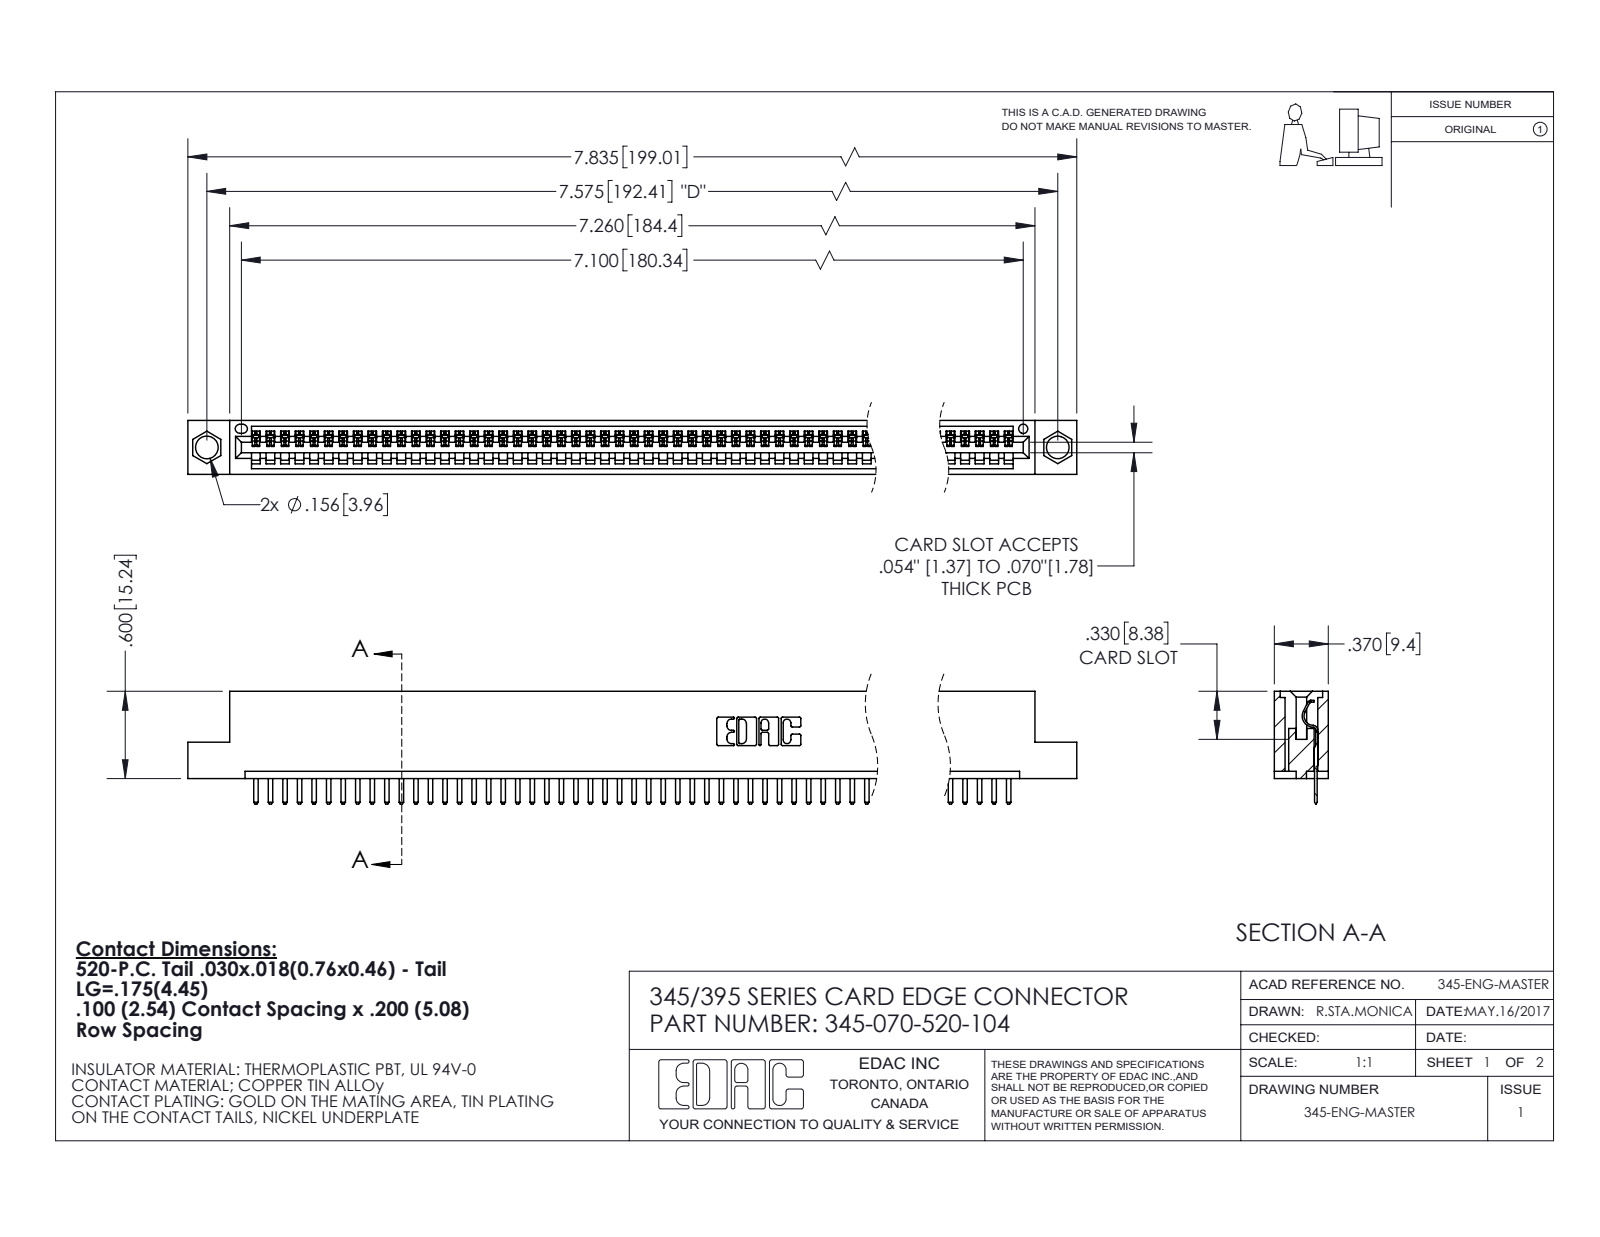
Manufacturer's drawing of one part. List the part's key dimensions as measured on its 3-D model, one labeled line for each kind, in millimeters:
Part name (STEP PRODUCT): 345-070-520-104; 345 Part_Flush Mounting Lugs - 0.156 Dia-TI; 345-292-001_345-293-120
STEP written by: SolidWorks 2020 (CONFIG_CONTROL_DESIGN)
Units: millimetres
Bodies: 71 solids, 4480 faces (3034 planar, 1446 cylindrical, 0 other)
Overall size (bounding box): 199 × 19.7 × 9.4
Volume: 18 830 mm³ · Surface area: 24 580 mm²
Round holes (diameter × count): ⌀4 ×2, ⌀1.6 ×1
Partial cylindrical surfaces — rounded edges, fillets, slot ends (radius × count): R0.3 ×142, R0.2 ×140, R0.3 ×22, R0.2 ×6, R0.8 ×6, R0.7 ×3, R0.8 ×2, R1 ×2
Main face-to-face distances: 7.6, 1.8, 9.4, 5.1, 2.5, 6.9, 0.6, 5.7, 1.8, 3.8
Hole centre spacings: 6.9, 186.4, 192.4
